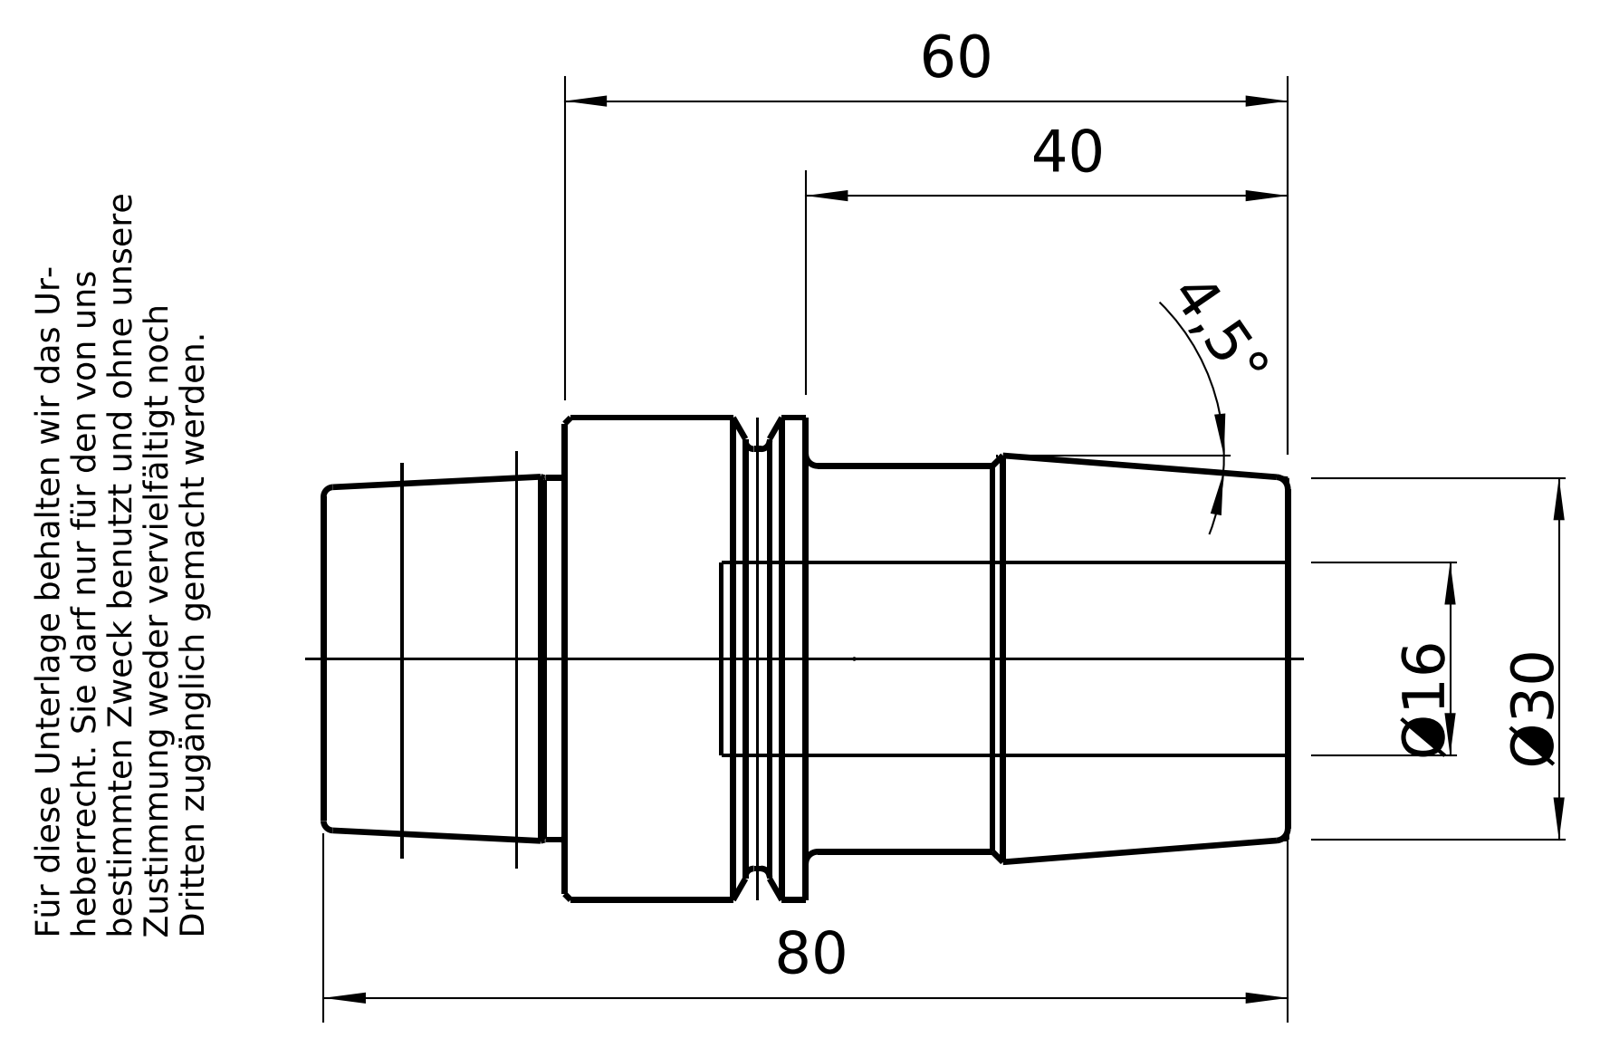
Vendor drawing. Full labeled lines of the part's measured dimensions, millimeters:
Part name (STEP PRODUCT): E40-145-16
STEP written by: PRO/ENGINEER BY PARAMETRIC TECHNOLOGY CORPORATION, 2010430 (CONFIG_CONTROL_DESIGN)
Units: millimetres
Bodies: 1 solid, 68 faces (8 planar, 18 cylindrical, 42 other)
Overall size (bounding box): 79.9 × 40 × 40
Volume: 48 962 mm³ · Surface area: 15 512 mm²
Round holes (diameter × count): ⌀16 ×1, ⌀21.04 ×1, ⌀25.57 ×1
Round bosses / shafts (diameter × count): ⌀40 ×1, ⌀34.75 ×1, ⌀32 ×1, ⌀29.81 ×1
Main face-to-face distances: 60, 19.95, 40.05, 7.95, 12, 52.05, 13, 5.05, 6.95, 47
